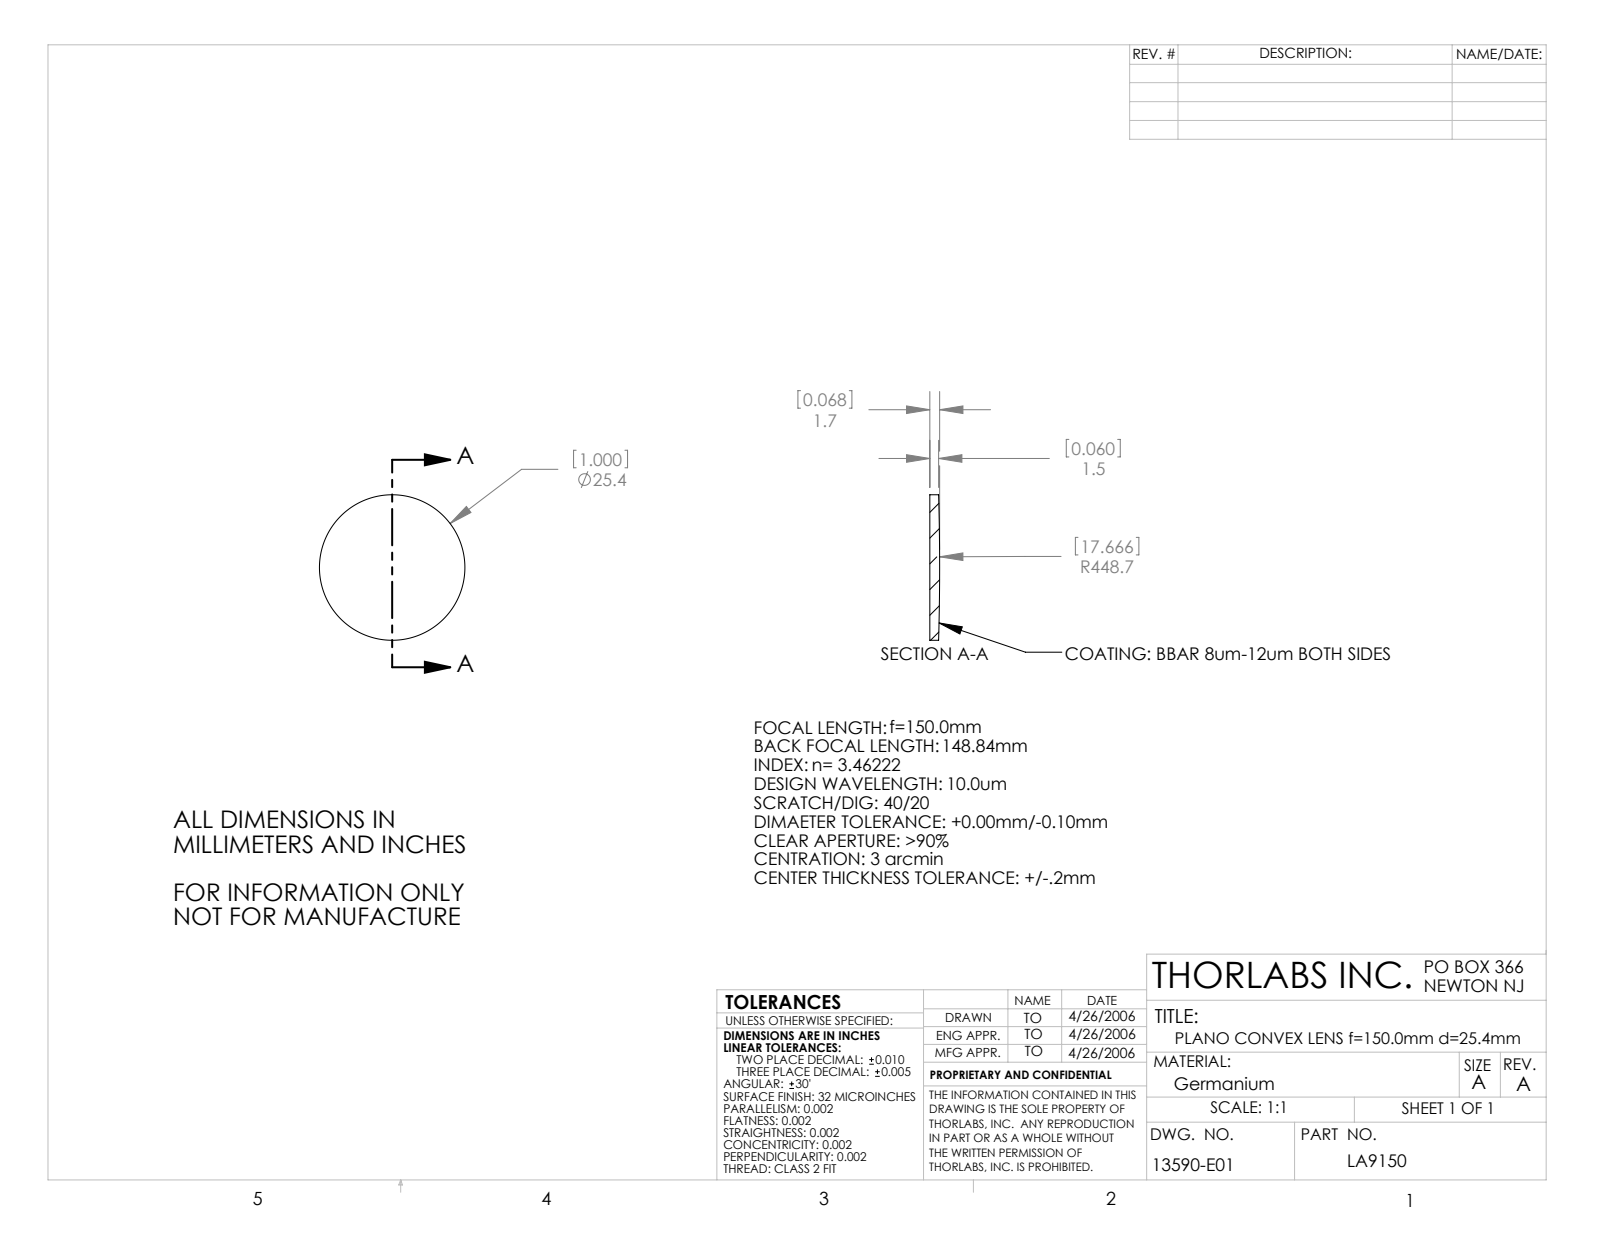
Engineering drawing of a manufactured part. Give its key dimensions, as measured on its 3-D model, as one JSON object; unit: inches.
{"part_name": "13590-E0W", "step_written_by": "SolidWorks 2007 (AUTOMOTIVE_DESIGN)", "units": "inches", "bodies": {"solids": 0, "faces": 5, "planar": 1, "cylindrical": 2, "other": 2}, "overall_size": [1, 1, 0.068], "round_bosses_or_shafts": [[1, 1]]}
